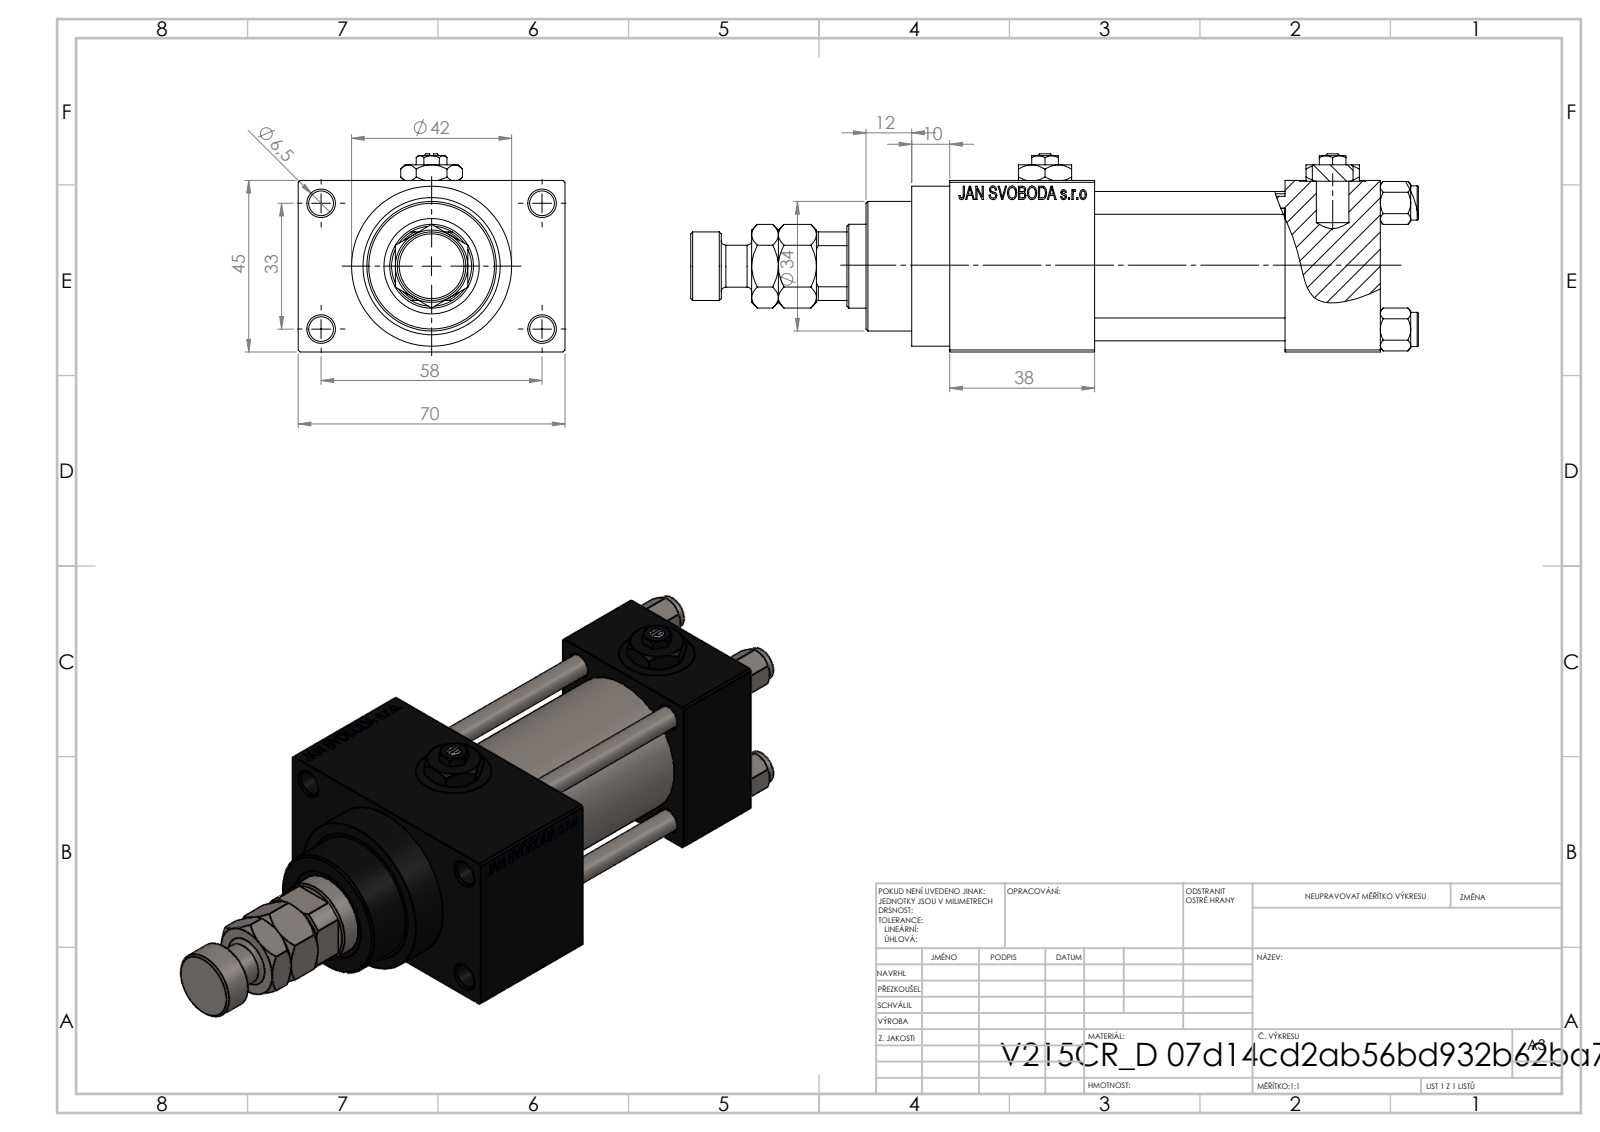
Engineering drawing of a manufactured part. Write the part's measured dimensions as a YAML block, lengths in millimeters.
part_name: "NUT_M5_D; V215_VC_A; Zatka_pro_OIL_PORT; V215CR_D_TYCINKA (+3 more)"
step_written_by: "SolidWorks 2019 (CONFIG_CONTROL_DESIGN)"
units: millimeters
bodies: {solids: 14, faces: 1255, planar: 558, cylindrical: 103, other: 594}
overall_size: [191, 70, 52]
volume: 249692
surface_area: 84321
round_holes:
  - {diameter: 6, count: 4}
  - {diameter: 6.5, count: 4}
  - {diameter: 13.16, count: 4}
  - {diameter: 20, count: 4}
  - {diameter: 7, count: 3}
  - {diameter: 10.5, count: 1}
  - {diameter: 22, count: 1}
  - {diameter: 24, count: 1}
  - {diameter: 25, count: 1}
  - {diameter: 32, count: 1}
  - {diameter: 33, count: 1}
round_bosses_or_shafts:
  - {diameter: 9, count: 4}
  - {diameter: 42, count: 1}
  - {diameter: 38, count: 1}
  - {diameter: 34, count: 1}
  - {diameter: 18, count: 1}
  - {diameter: 11, count: 1}
partial_cylinders:
  - {radius: 10.5, count: 1}
face_to_face_distances: [45, 25, 50, 12.5, 75, 57.5, 88, 38, 113, 70]
hole_center_spacings: [12.4, 23.48, 33.2, 33.37, 35.35, 45.6, 56.35, 33]
